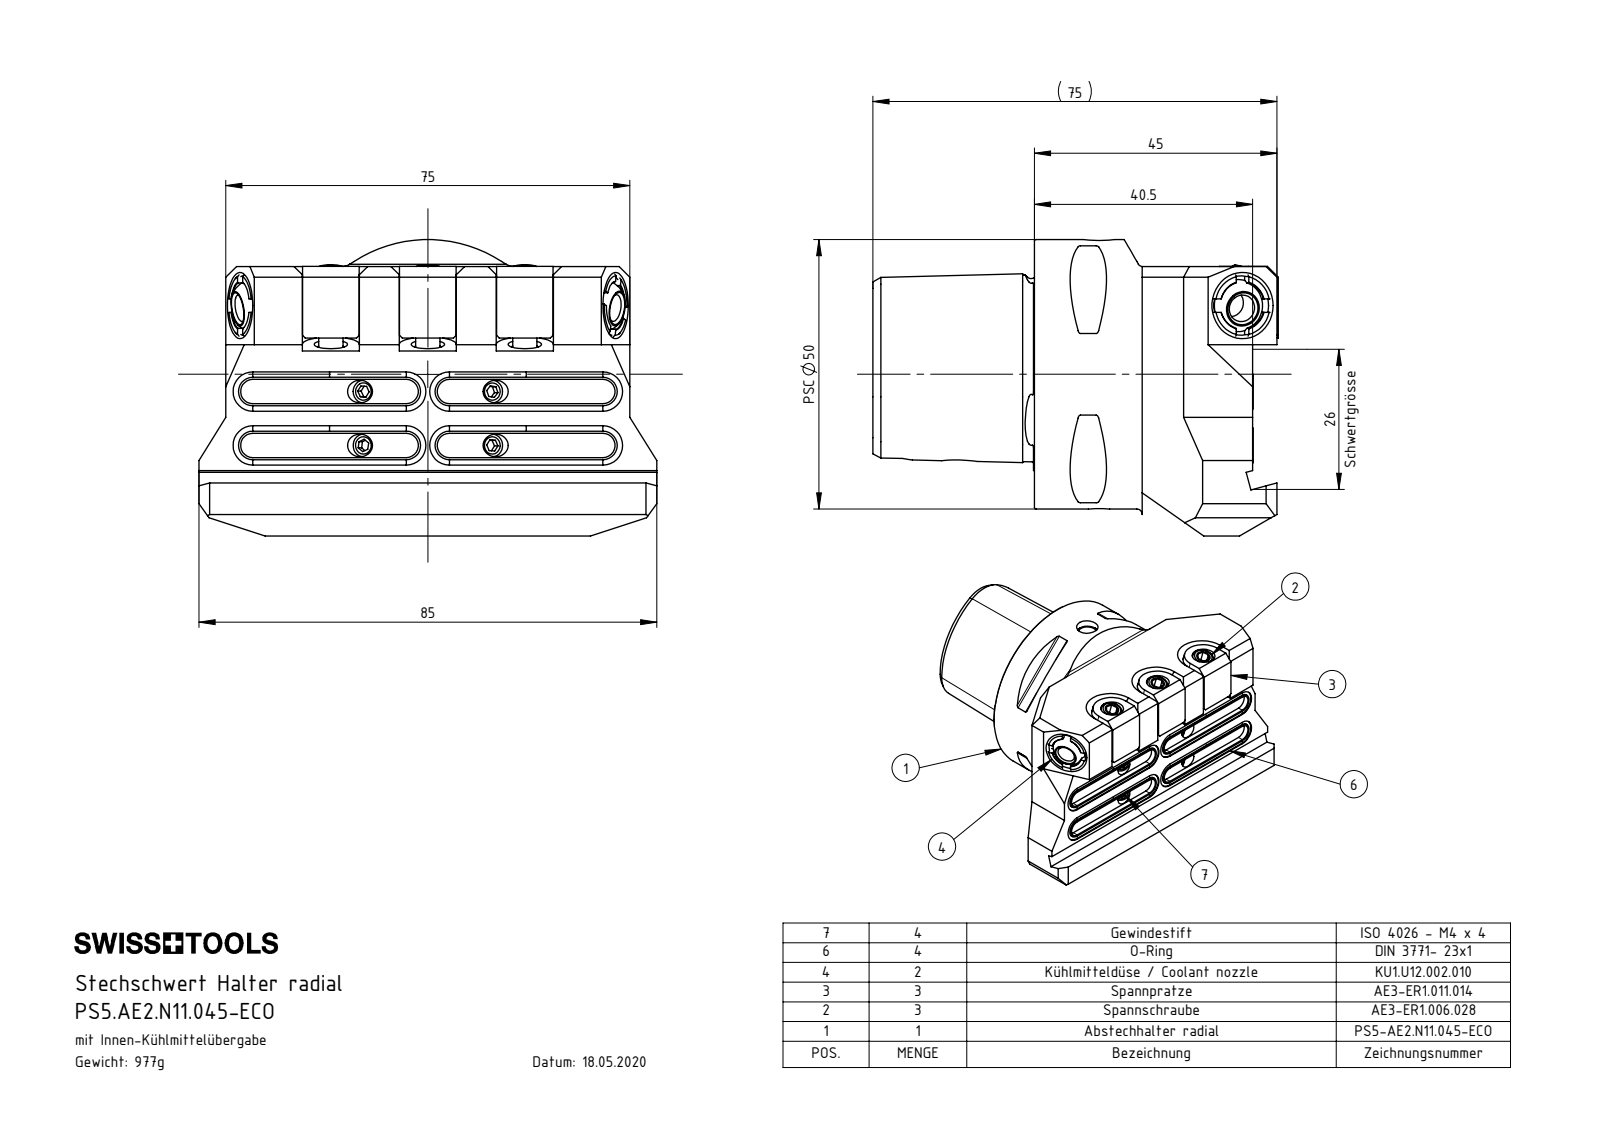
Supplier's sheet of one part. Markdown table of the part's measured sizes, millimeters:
| quantity | value |
| --- | --- |
| part name | S5-.E2.N11.045-ECO; KU1-U12.002.010_A; KVT_MB_600_060; KU1-U12.003.010_B (+7 more) |
| STEP written by | SolidWorks 2017 (AUTOMOTIVE_DESIGN) |
| units | millimeters |
| bodies | 23 solids, 756 faces (274 planar, 210 cylindrical, 272 other) |
| overall size | 85 × 75.12 × 55 |
| volume | 126 796 mm³ |
| surface area | 35 678 mm² |
| round holes (diameter × count) | 5 × 8, 3.3 × 4, 4.2 × 4, 3 × 3, 5.5 × 3, 6.2 × 3, 10 × 2, 11 × 2, 4 × 1, 6.1 × 1, 14.5 × 1, 21 × 1 |
| round bosses / shafts (diameter × count) | 6 × 4, 4 × 4, 1 × 4, 4.5 × 3, 12 × 2, 50 × 1 |
| partial cylindrical surfaces (radius × count) | 0.5 × 8, 2.25 × 8, 2.65 × 8, 3.65 × 8, 5.25 × 3, 5.3 × 3, 4.4 × 2, 0.8 × 1 |
| main face-to-face distances | 50, 4.5, 18, 40.5, 45, 20, 75, 1.5, 6, 39 |
| hole center spacings | 10, 18, 26, 36 |
